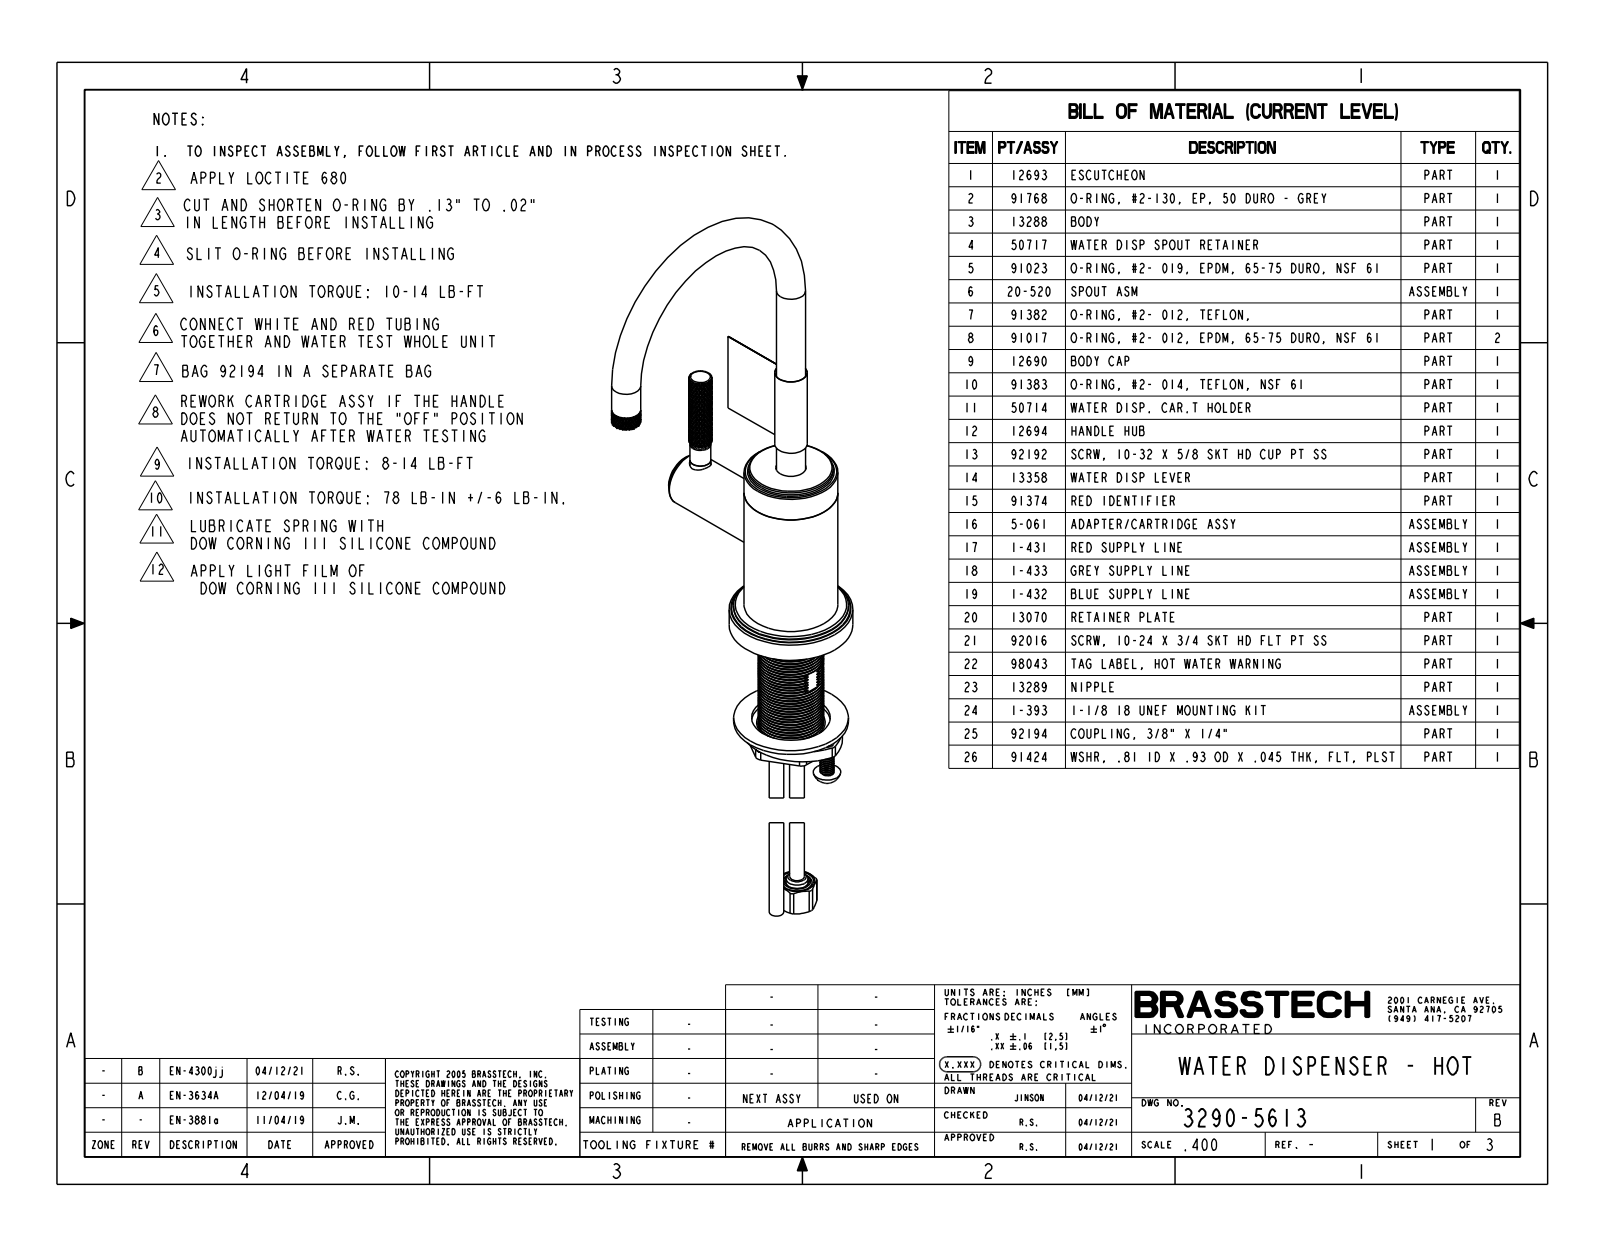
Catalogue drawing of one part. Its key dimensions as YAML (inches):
part_name: "3290-5613"
step_written_by: "CREO PARAMETRIC BY PTC INC, 2018400 (CONFIG_CONTROL_DESIGN)"
units: inches
bodies: {solids: 1, faces: 3509, planar: 39, cylindrical: 690, other: 2780}
overall_size: [9.275, 5.313, 3.648]
volume: 10.88
surface_area: 50.41
round_holes:
  - {diameter: 0.375, count: 1}
  - {diameter: 1, count: 1}
round_bosses_or_shafts:
  - {diameter: 0.5, count: 2}
  - {diameter: 2.125, count: 1}
  - {diameter: 1.975, count: 1}
  - {diameter: 1.61, count: 1}
  - {diameter: 1.45, count: 1}
  - {diameter: 0.95, count: 1}
  - {diameter: 0.8, count: 1}
  - {diameter: 0.4, count: 1}
face_to_face_distances: [3.306, 0.425, 2.881, 3.227, 2.802, 0.079, 6.275, 5.85, 3.048, 2.969]
